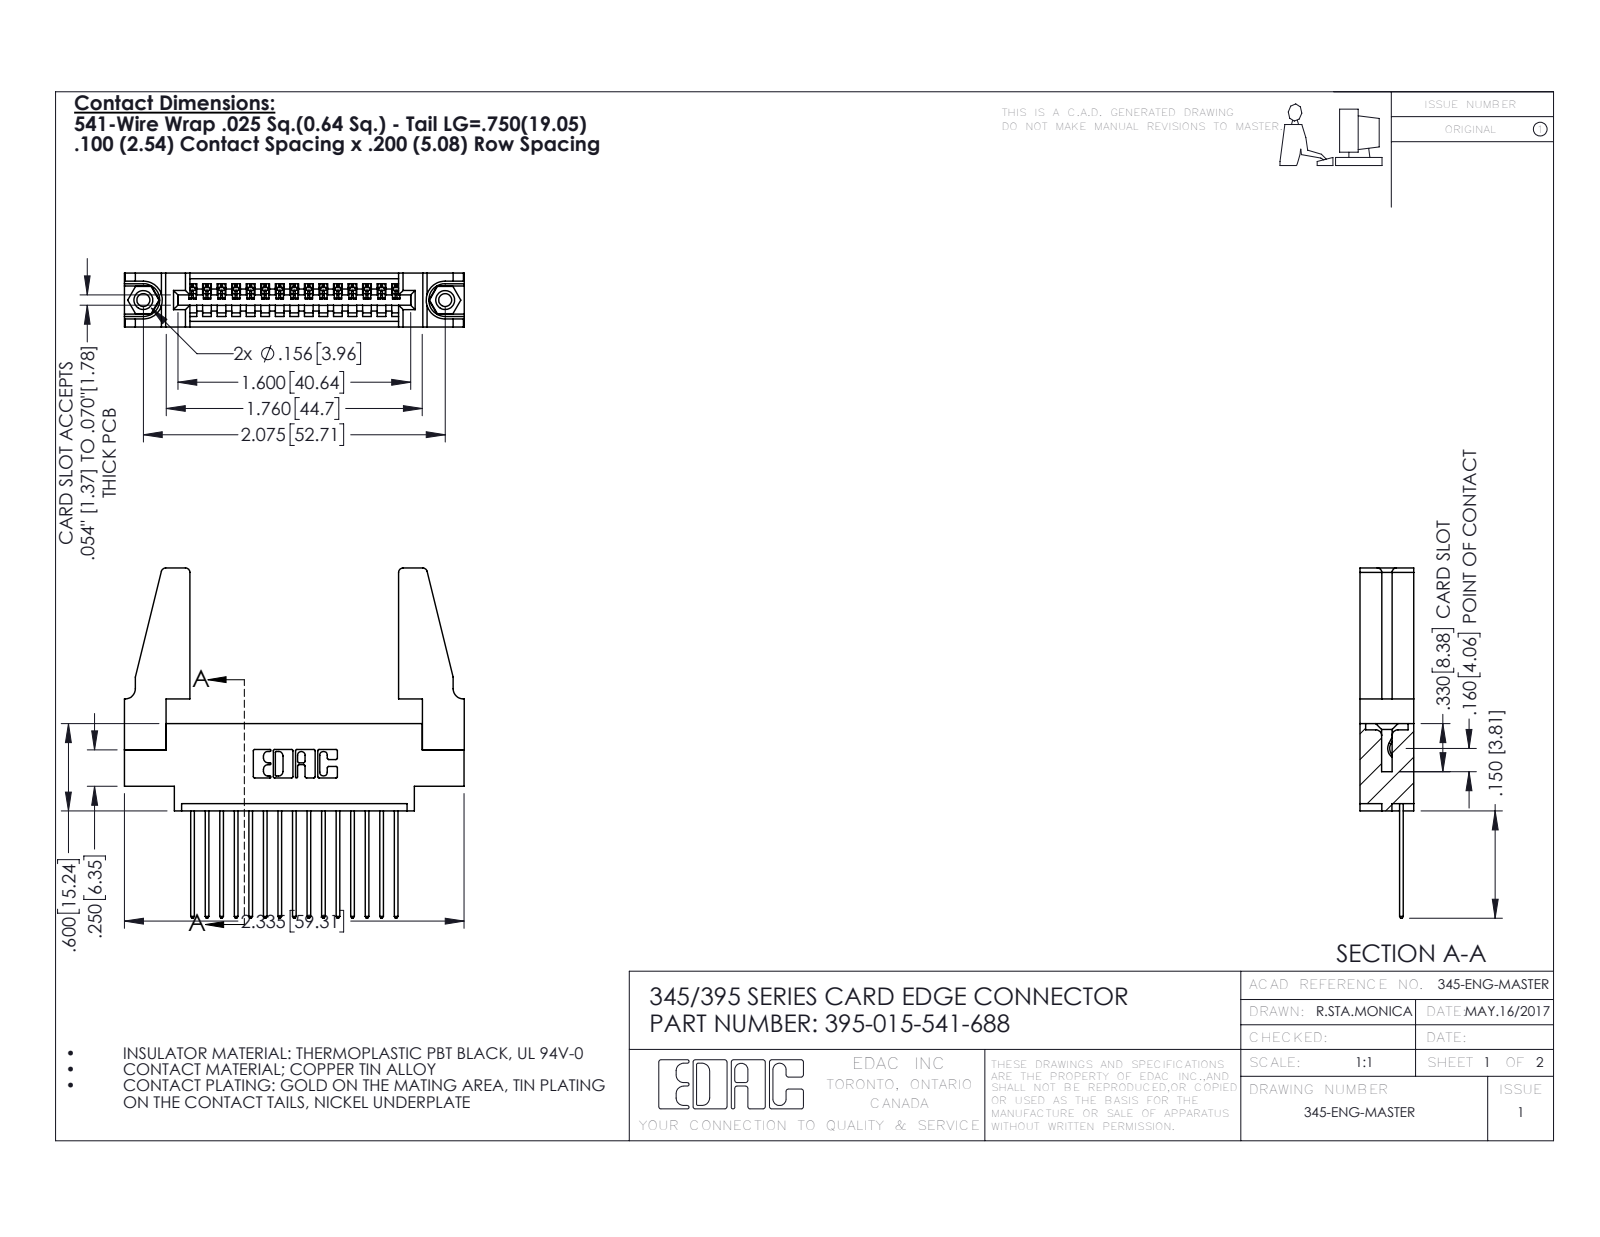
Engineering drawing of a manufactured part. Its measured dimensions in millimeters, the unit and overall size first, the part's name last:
Units: millimetres
Overall size (bounding box): 61.1 × 59.3 × 9.4
Round holes (diameter × count): ⌀2.3 ×2, ⌀3.2 ×2, ⌀4 ×2, ⌀1.6 ×1
Round bosses / shafts (diameter × count): ⌀3.9 ×2
Partial cylindrical surfaces — rounded edges, fillets, slot ends (radius × count): R0.2 ×30, R0.3 ×30, R0.3 ×22, R0.8 ×8, R0.2 ×6, R0.8 ×6, R0.7 ×3, R0.8 ×2
Main face-to-face distances: 9.4, 1.8, 7.6, 2.5, 6.9, 0.6, 5.1, 5.7, 3.8, 3.8
Hole centre spacings: 6.9, 46.8, 52.7
Volume: 8 600 mm³ · Surface area: 10 290 mm²
Bodies: 20 solids, 1124 faces (756 planar, 352 cylindrical, 16 other)
Part name (STEP PRODUCT): 345-292-001_345-293-141; 345-250-001_345-250-001-102; 395-015-541-688; 345-220-078_345-220-088 (+1 more)
STEP written by: SolidWorks 2016 (CONFIG_CONTROL_DESIGN)
